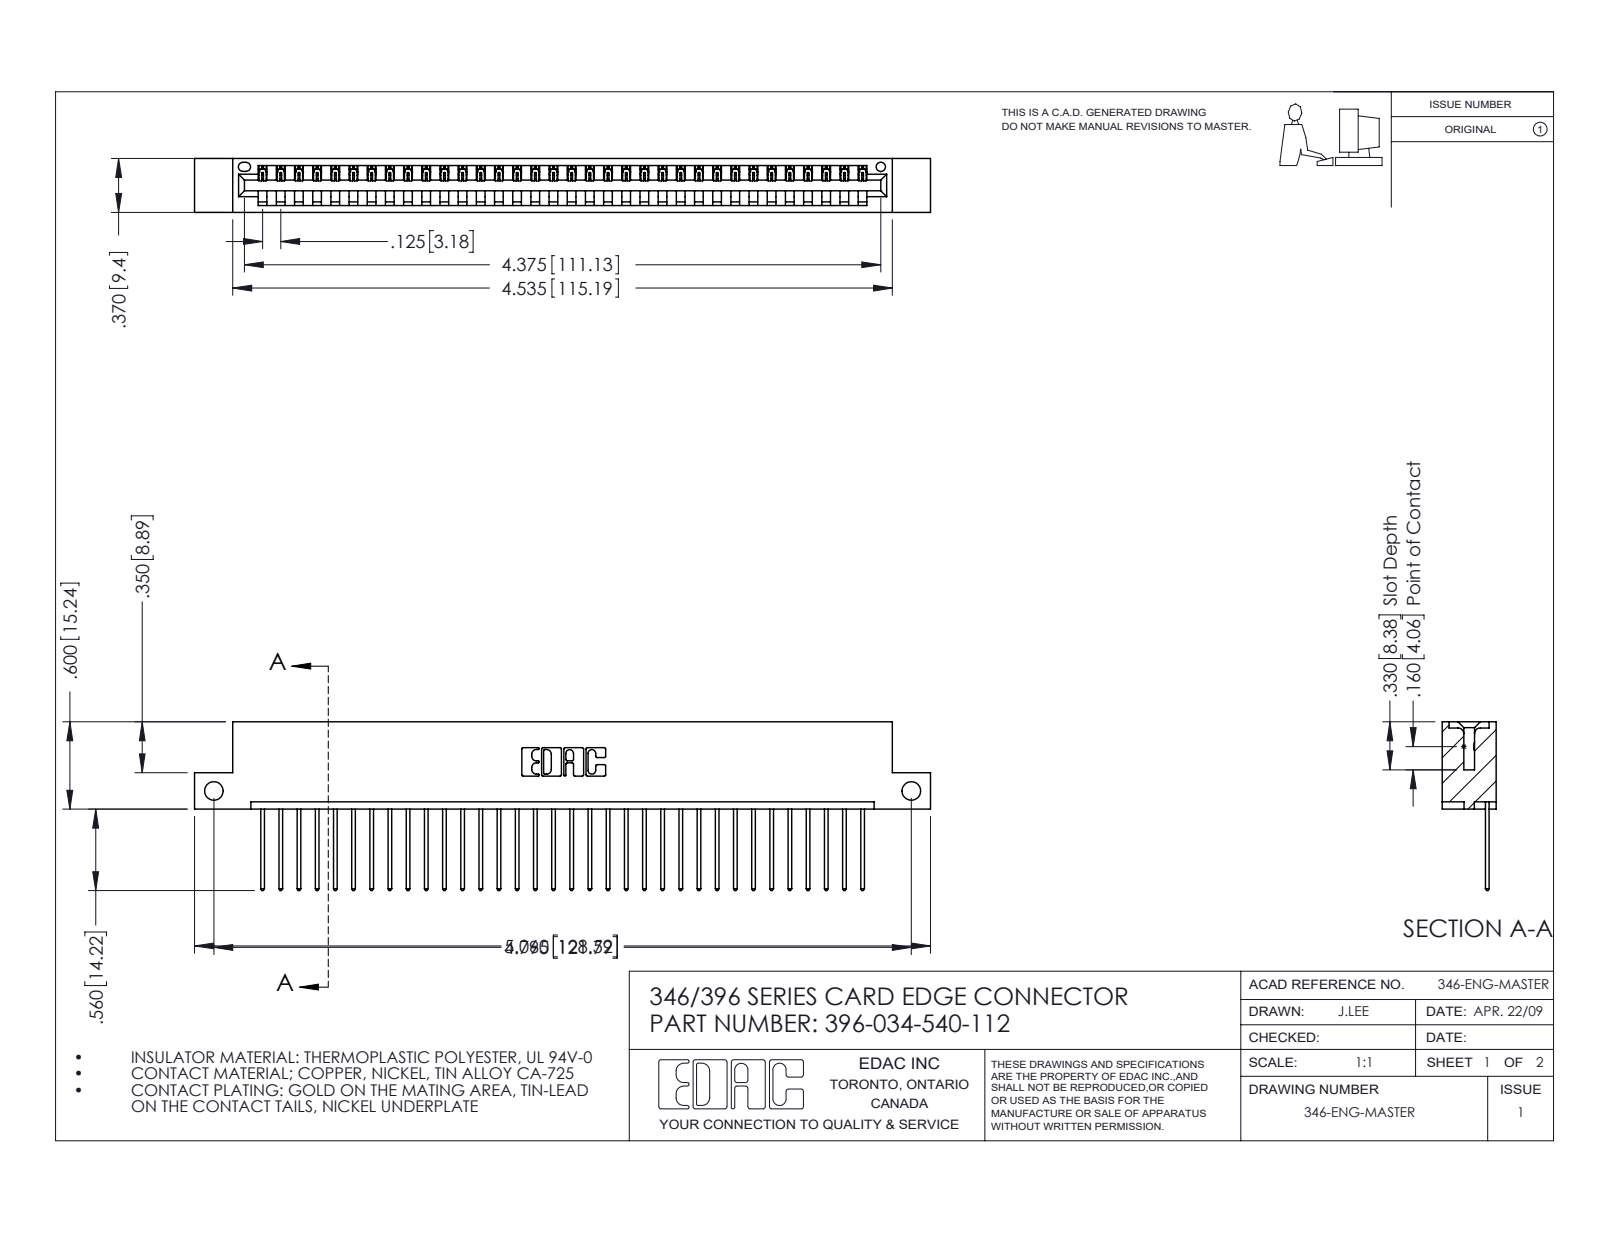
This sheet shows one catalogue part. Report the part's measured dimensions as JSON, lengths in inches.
{"part_name": "345-292-001_345-293-140; 396-034-540-112; 346 Part_Flush Mounting Lugs - Side Mount", "step_written_by": "SolidWorks 2016 (CONFIG_CONTROL_DESIGN)", "units": "inches", "bodies": {"solids": 35, "faces": 2094, "planar": 1436, "cylindrical": 658, "other": 0}, "overall_size": [5.06, 1.16, 0.37], "volume_in3": 0.745, "surface_area_in2": 23.81, "round_holes": [[0.128, 2], [0.064, 1]], "partial_cylinders_radius": [[0.006, 68], [0.01, 68], [0.01, 22], [0.007, 6], [0.031, 6], [0.026, 3], [0.031, 2], [0.04, 2]], "face_to_face_distances": [0.048, 0.322, 0.37, 0.25, 0.072, 0.298, 0.025, 0.148, 0.222, 0.1], "hole_center_spacings": [4.795]}
